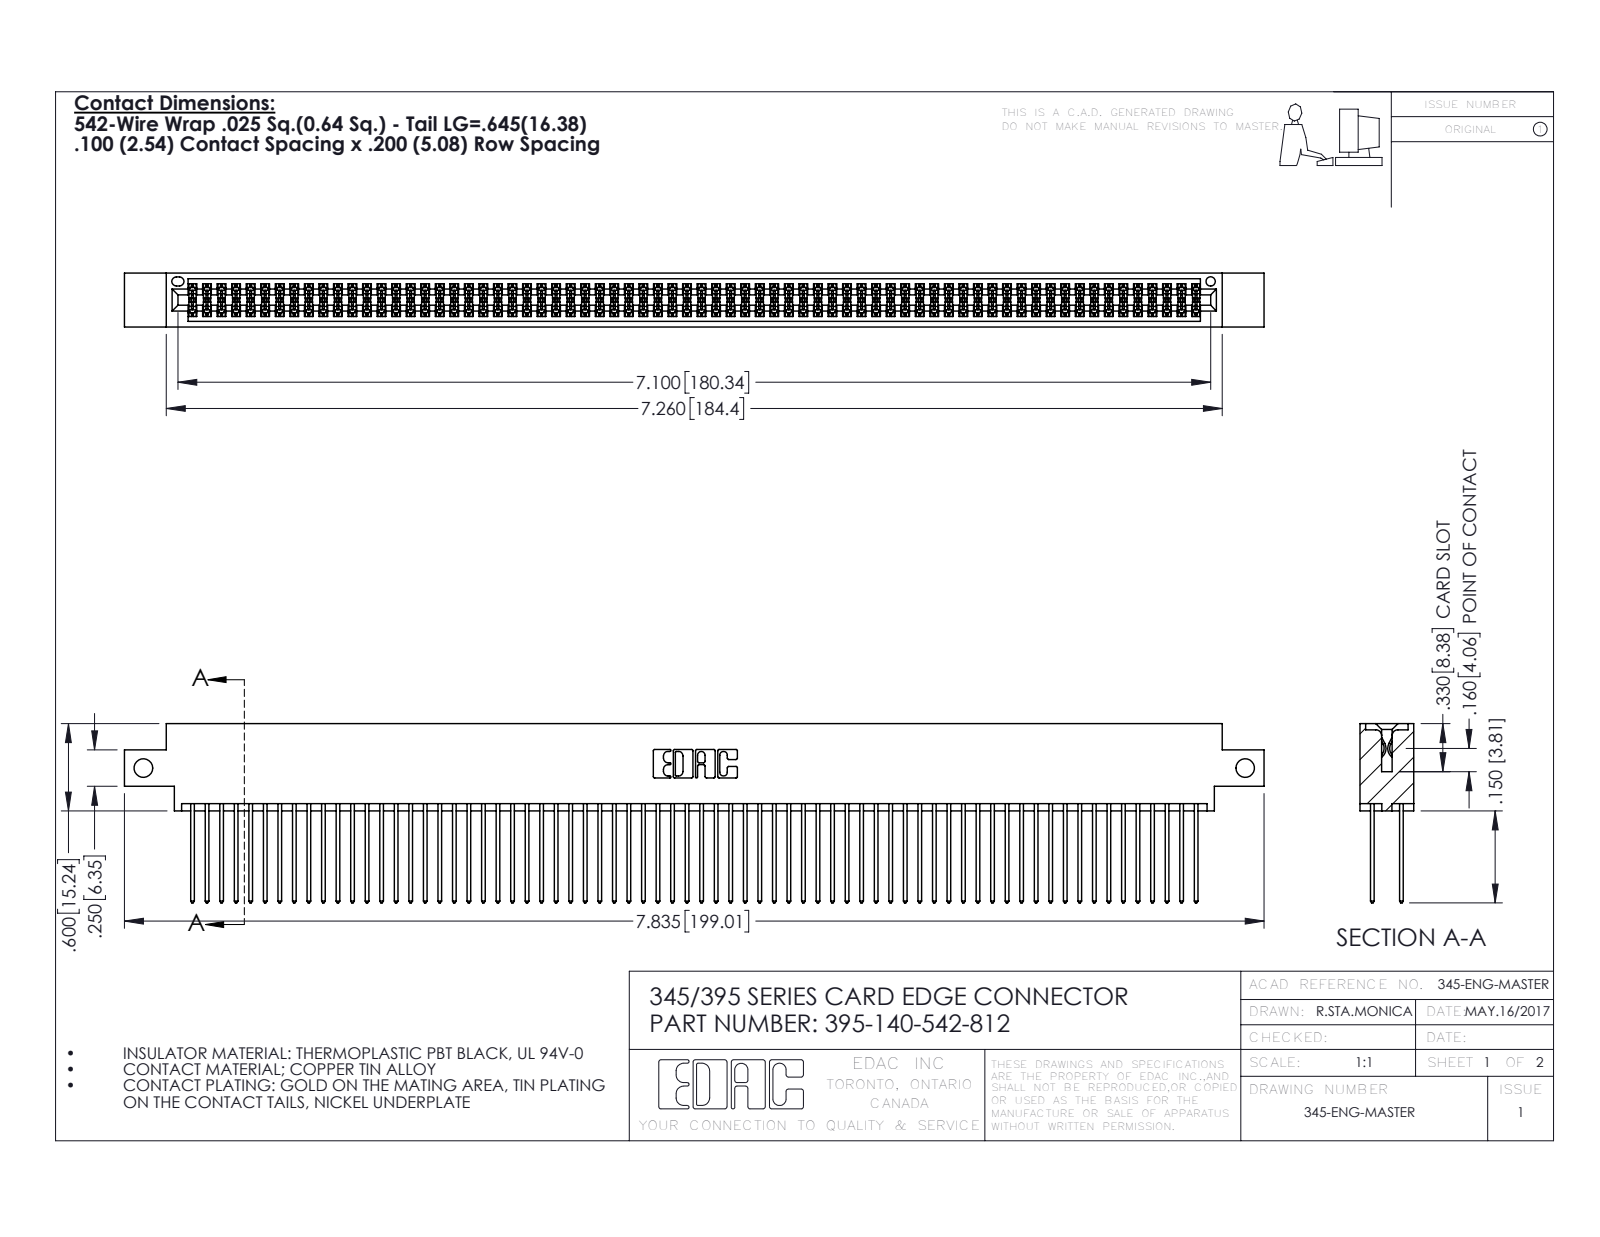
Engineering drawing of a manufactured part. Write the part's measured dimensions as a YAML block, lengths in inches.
part_name: "345 Part_0.170 Offset - Side Mount; 395-140-542-812; 345-292-001_345-293-142"
step_written_by: "SolidWorks 2016 (CONFIG_CONTROL_DESIGN)"
units: inches
bodies: {solids: 141, faces: 7130, planar: 4704, cylindrical: 2426, other: 0}
overall_size: [7.835, 1.232, 0.37]
volume: 1.223
surface_area: 51.5
round_holes:
  - {diameter: 0.128, count: 2}
  - {diameter: 0.064, count: 1}
partial_cylinders:
  - {radius: 0.006, count: 210}
  - {radius: 0.01, count: 140}
  - {radius: 0.01, count: 22}
  - {radius: 0.007, count: 6}
  - {radius: 0.031, count: 6}
  - {radius: 0.026, count: 3}
  - {radius: 0.014, count: 2}
  - {radius: 0.019, count: 2}
face_to_face_distances: [0.072, 0.298, 0.2, 0.098, 0.272, 0.025, 0.37, 0.225, 0.175, 0.149]
hole_center_spacings: [7.575]
